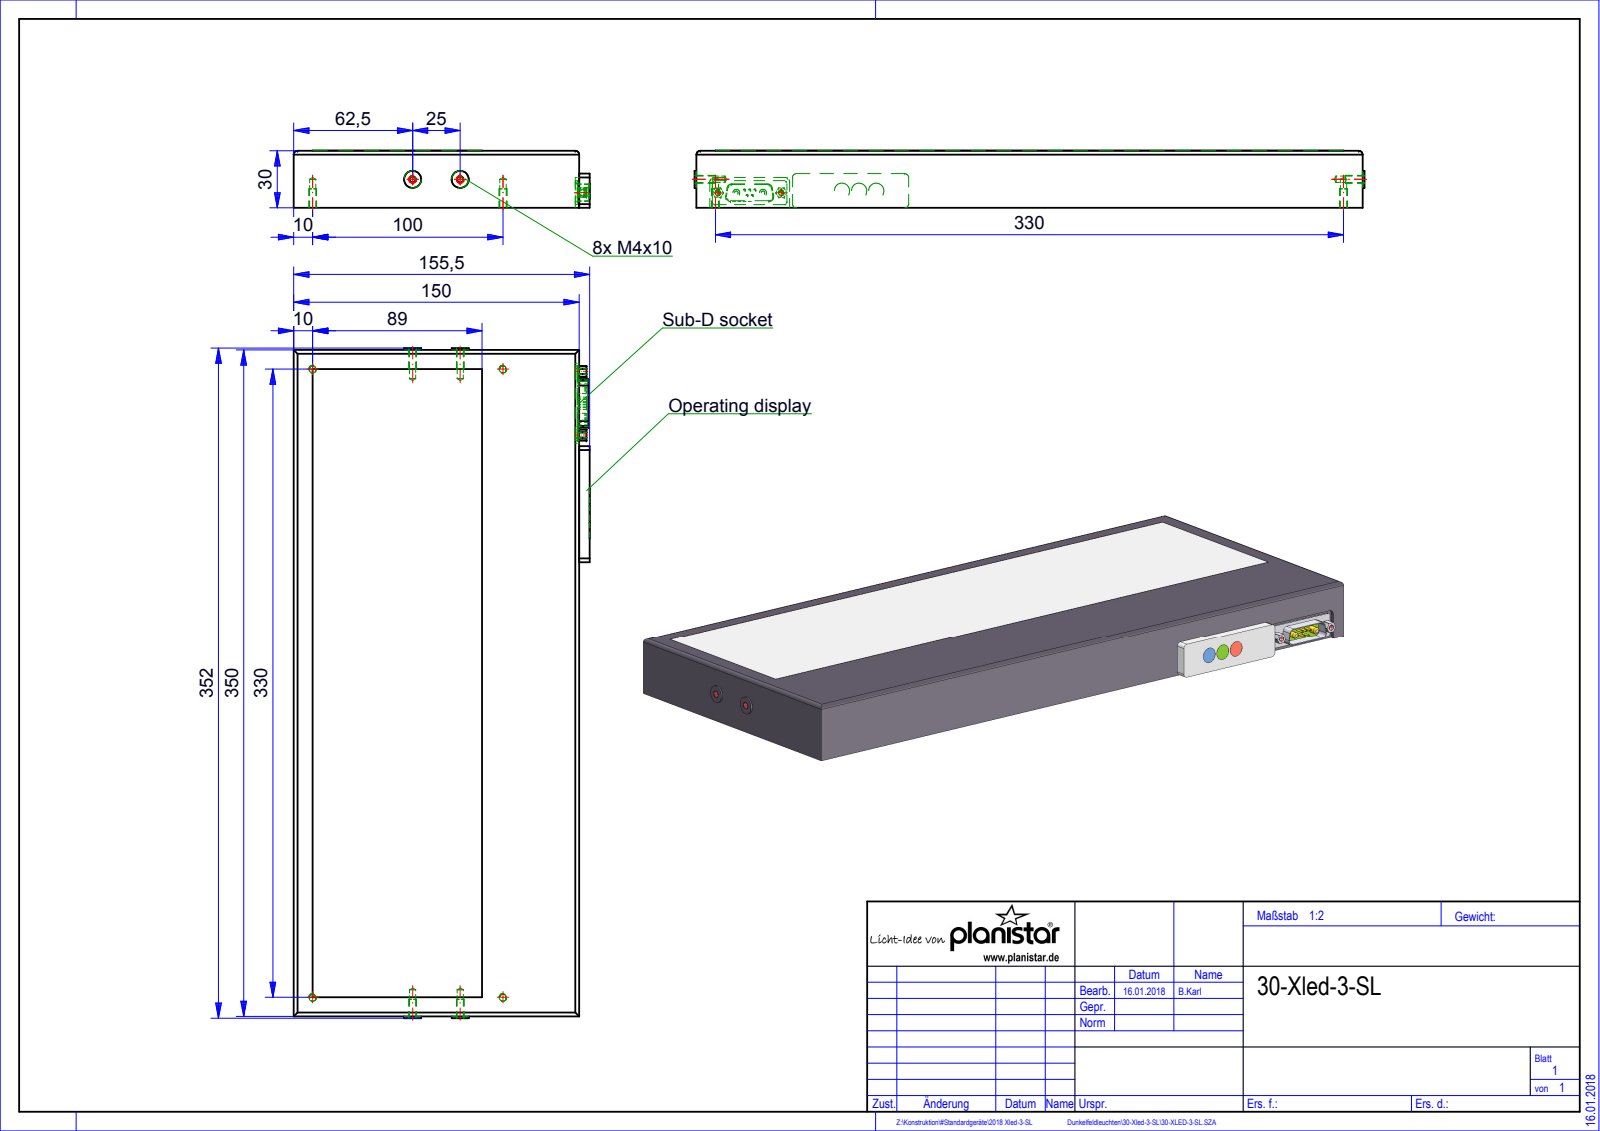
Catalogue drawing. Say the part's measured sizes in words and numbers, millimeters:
The part is named "Root; Baugruppe_Xled-2-VD; QUADER_0; Baugruppe_Baugruppe (+5 more)". Its 3-D file was written by "HiCAD 2015 2002.1 Build 408 (AUTOMOTIVE_DESIGN)". It is 12 solids with 169 faces: 84 planar, 68 cylindrical and 17 other. Overall it measures 352 by 155.55 by 30.1 millimeters. Its volume is 1 582 000 cubic millimeters and its surface area 141 259 square millimeters. Round holes: 6 of diameter 3.3, 6 of diameter 4, 2 of diameter 2.5, 2 of diameter 3. Round bosses or shafts: 5 of diameter 1, 3 of diameter 8, 2 of diameter 9, 2 of diameter 3.6. Partial cylindrical surfaces (rounded edges, fillets, slot ends): 12 of radius 0.2, 8 of radius 2, 6 of radius 2.5, 4 of radius 1.5, 4 of radius 2.1. The main face-to-face distances are 30.1, 30, 150, 350, 1, 2, 148, 155.5, 7.5, 5.5. The hole center spacings are 100, 330, 344.82, 25, 33.32.
